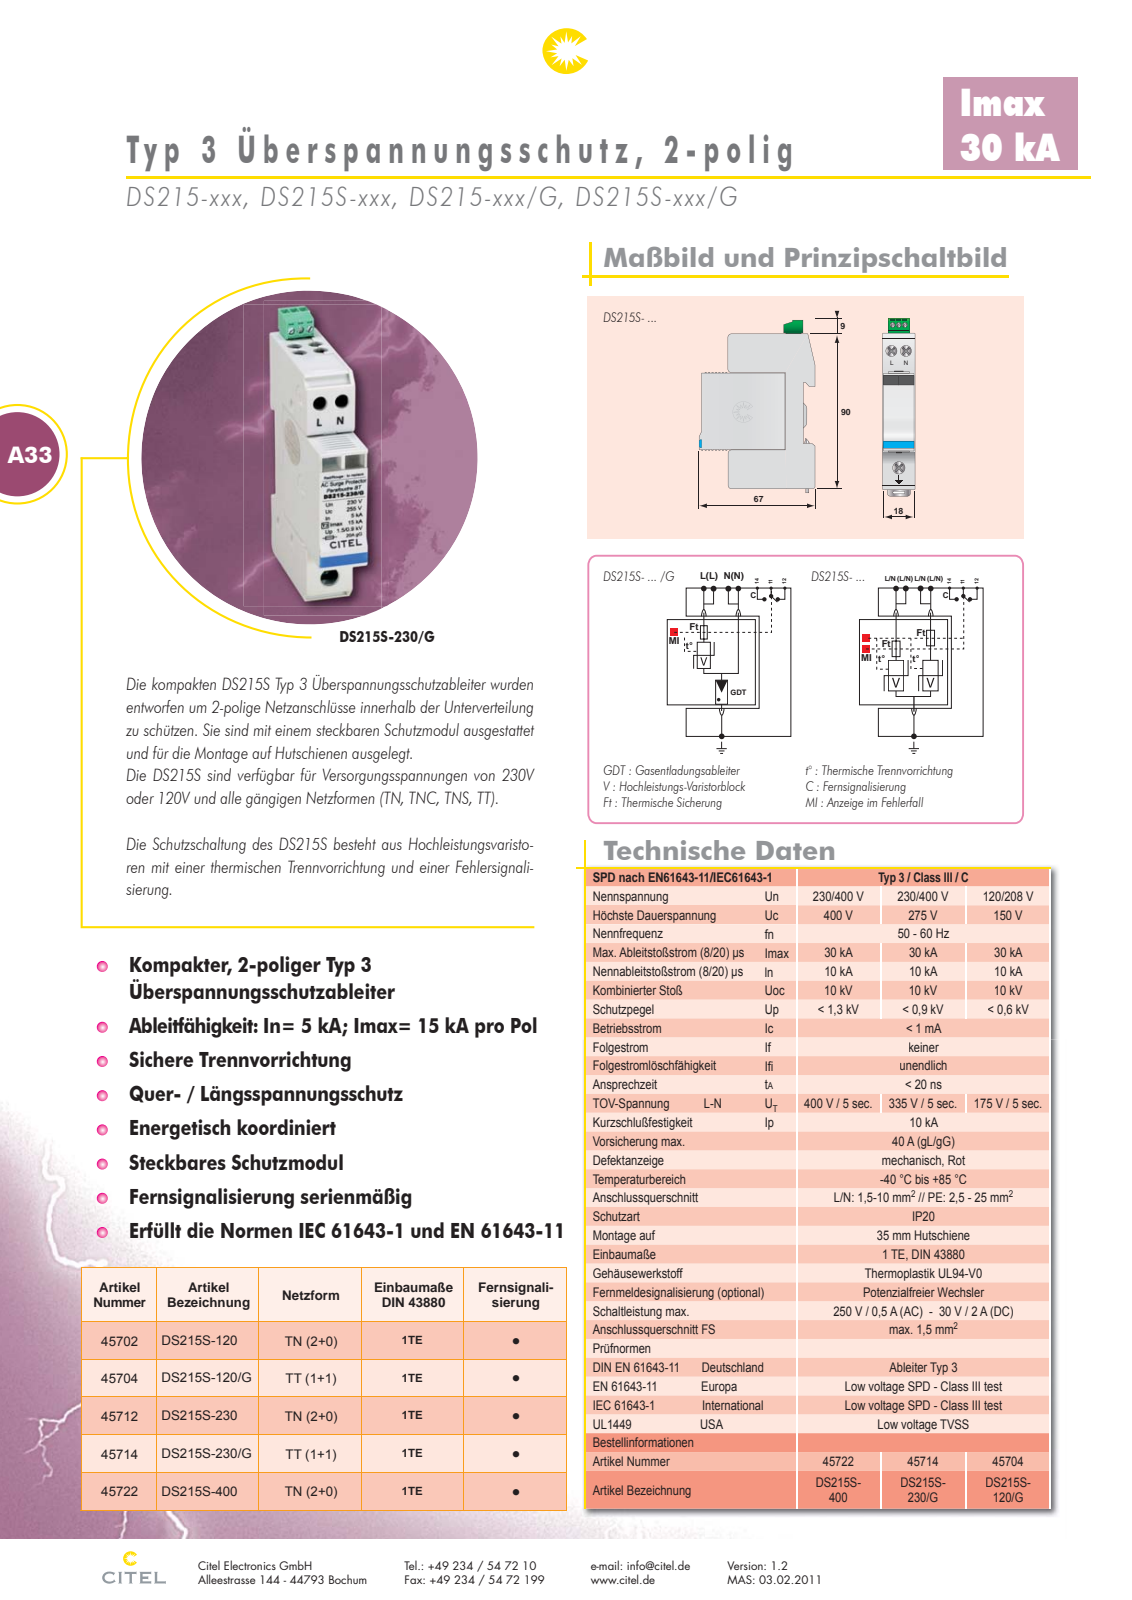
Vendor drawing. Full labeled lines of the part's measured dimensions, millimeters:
Part name (STEP PRODUCT): DS215S
STEP written by: Creo Elements/Direct Modeling 20.0AP0401 12-May-2017 (C) Parametric Technology GmbH (AUTOMOTIVE_DESIGN)
Units: millimetres
Bodies: 1 solid, 982 faces (700 planar, 197 cylindrical, 85 other)
Overall size (bounding box): 105.1 × 67.8 × 17.8
Volume: 85 590 mm³ · Surface area: 24 145 mm²
Round holes (diameter × count): ⌀5.4 ×4, ⌀2.8 ×3, ⌀3.2 ×3, ⌀5 ×3, ⌀5.3 ×2, ⌀7 ×1, ⌀8.5 ×1
Round bosses / shafts (diameter × count): ⌀2.4 ×3, ⌀1.6 ×3, ⌀6.8 ×2, ⌀10 ×1, ⌀7 ×1, ⌀5 ×1
Partial cylindrical surfaces — rounded edges, fillets, slot ends (radius × count): R0.5 ×47, R1.8 ×13, R0.2 ×9, R1 ×8, R1.5 ×6, R1.56 ×6, R1.6 ×6, R0.3 ×4
Main face-to-face distances: 17.8, 17.5, 67.5, 22.5, 6.7, 44.5, 1.6, 15.5, 66.3, 67.3
Hole centre spacings: 8, 3.5, 6.7, 10.44, 15.36, 69.37, 84.67, 7
